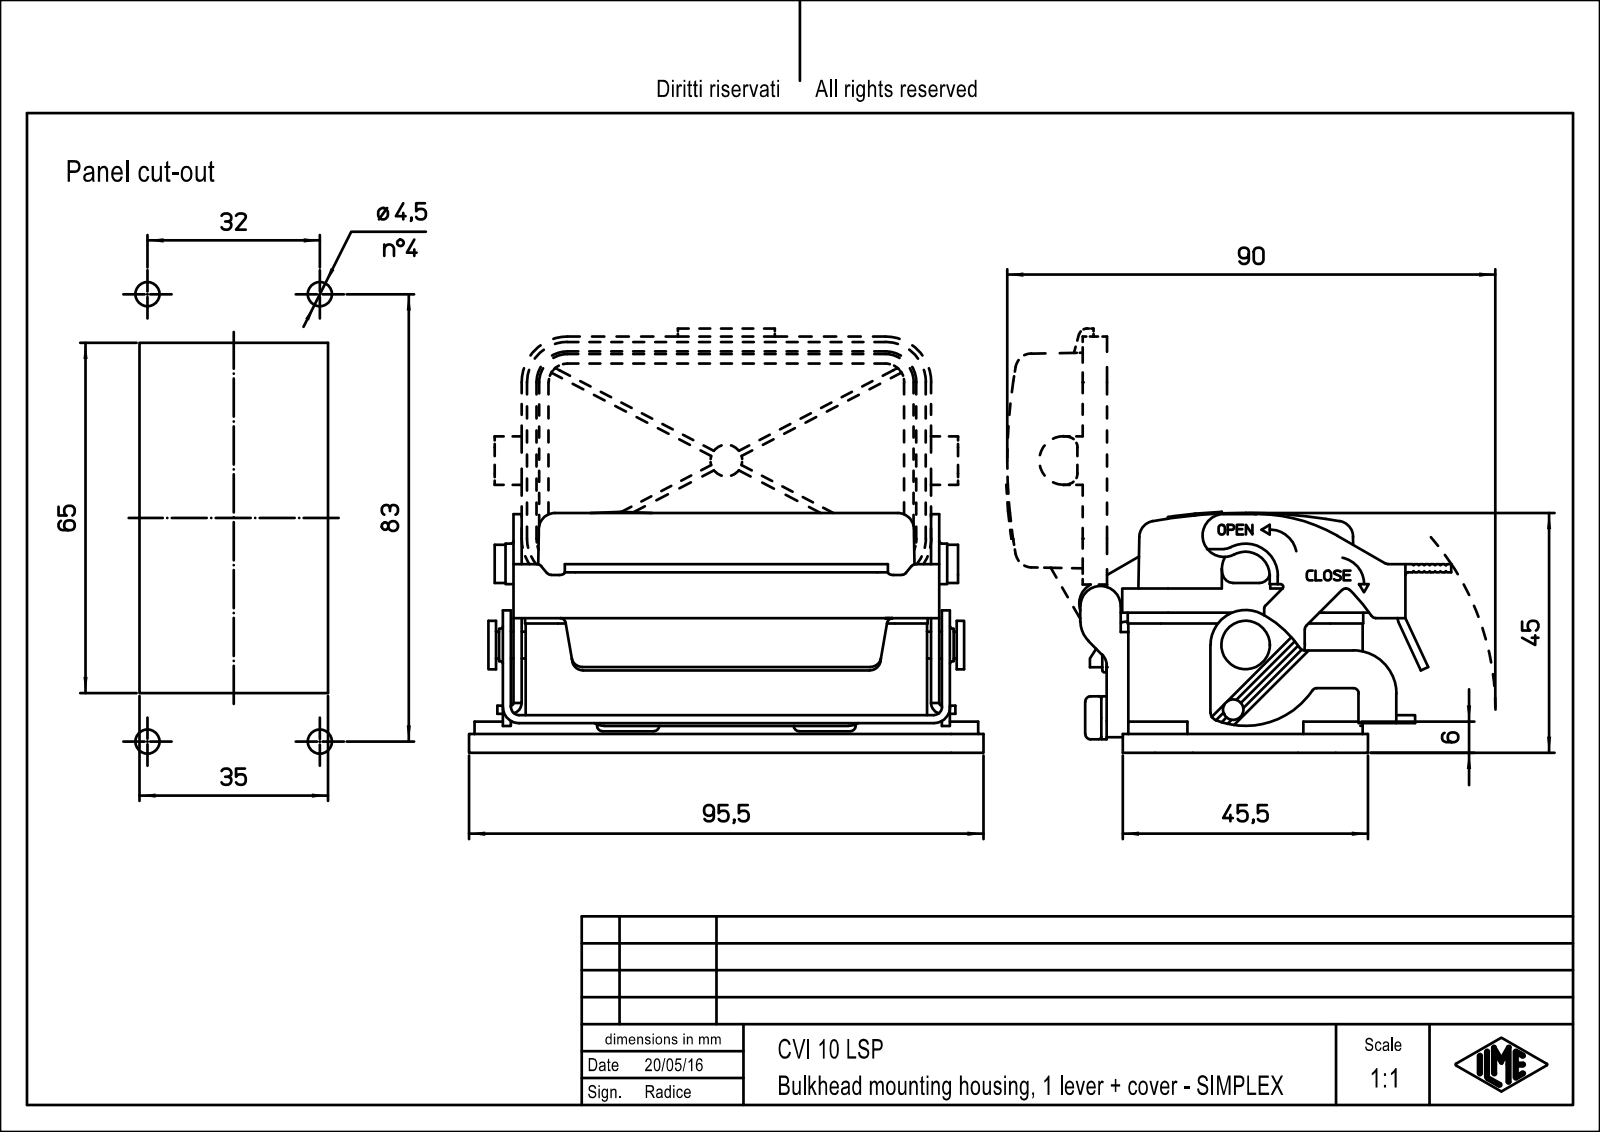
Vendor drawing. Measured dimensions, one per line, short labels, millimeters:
name: CVI_10_LSP
written by: Creo Elements/Direct Modeling 18.1F 24-Jul-2014 (C) Parametric Technology GmbH (AUTOMOTIVE_DESIGN)
unit: mm
bodies: 1 solid, 672 faces (351 planar, 285 cylindrical, 36 other)
size: 95.5 × 80.38 × 78.72
volume: 54 536 mm³; area: 46 266 mm²
holes: 4× ⌀2.46, 4× ⌀3, 4× ⌀4.5, 4× ⌀4.5
bosses: 3× ⌀0.8, 1× ⌀9, 1× ⌀8, 1× ⌀5, 1× ⌀2.4
rounds: 18× R3, 16× R0.25, 15× R0.33, 15× R1, 12× R0.5, 12× R1.5, 12× R2, 8× R6
face distances: 1.4, 2, 40.5, 5.5, 4, 1, 3.5, 3, 4.25, 79.6
hole spacings: 13.24, 32.24, 70.04, 75.96, 27, 32, 57, 63.07
